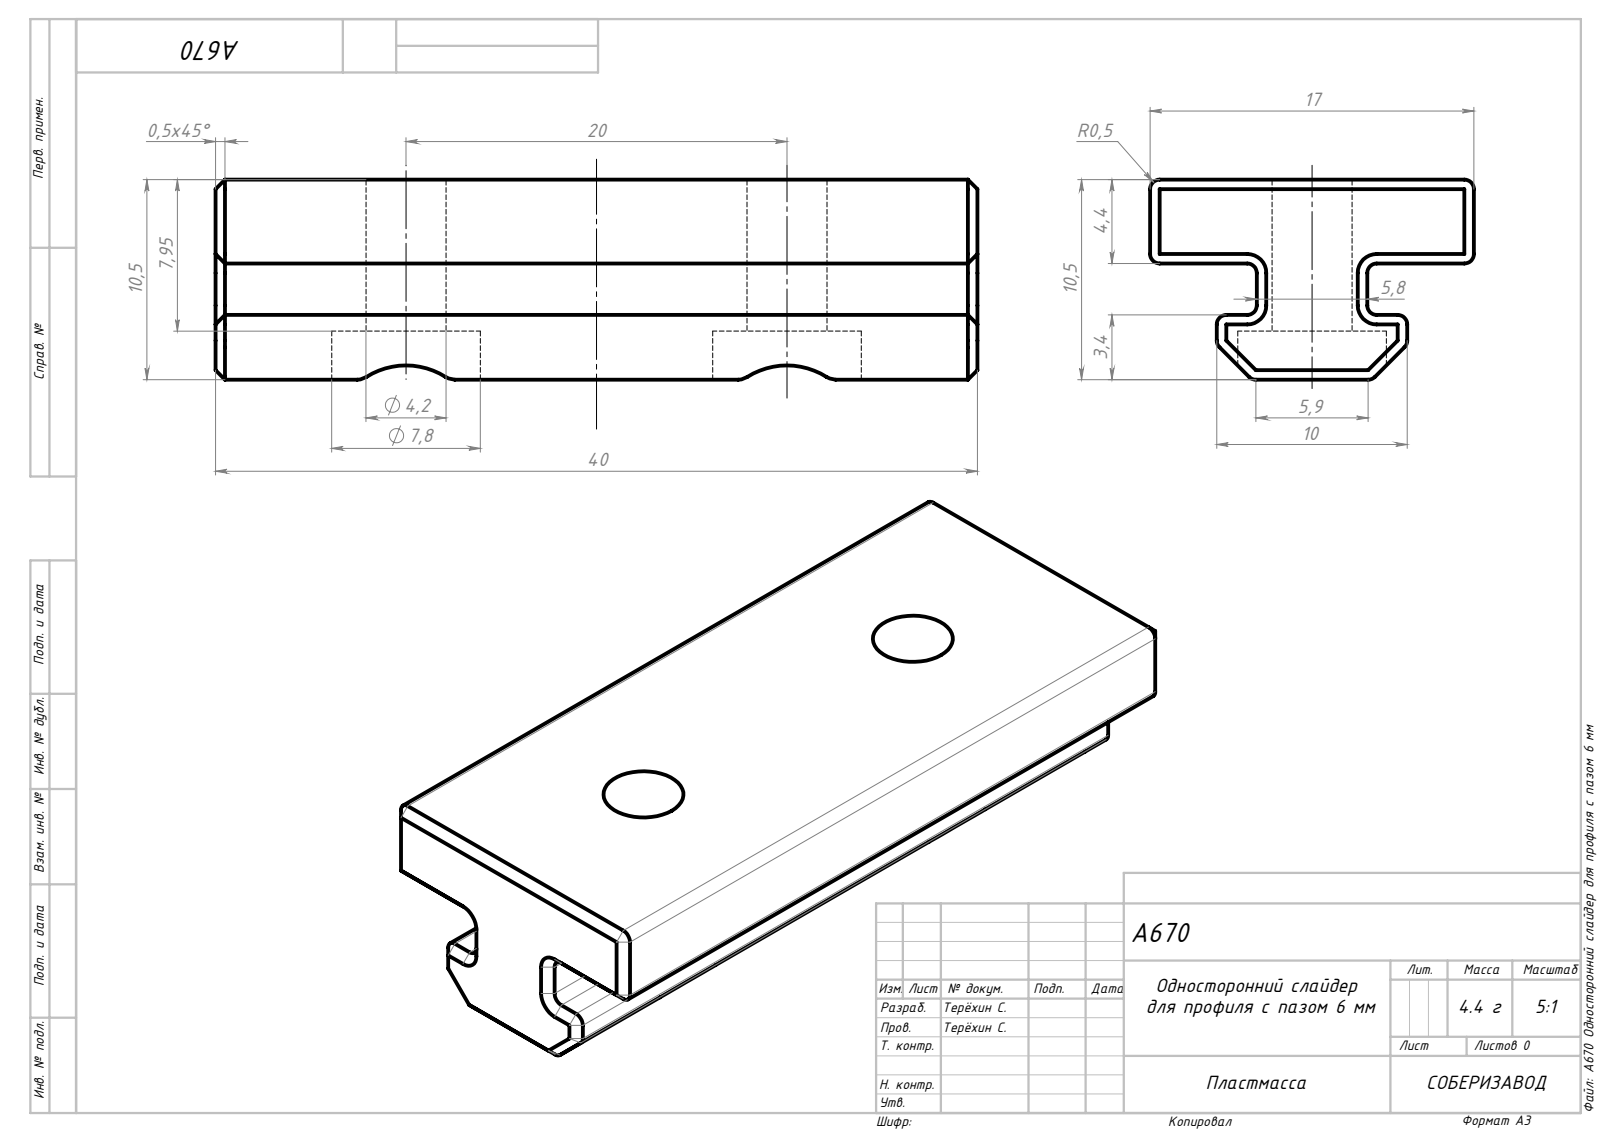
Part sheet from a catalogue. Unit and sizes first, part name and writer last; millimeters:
Units: millimetres
Overall size (bounding box): 40 × 20 × 10.5
Round holes (diameter × count): ⌀4.2 ×2, ⌀7.8 ×2
Partial cylindrical surfaces — rounded edges, fillets, slot ends (radius × count): R0.5 ×14
Main face-to-face distances: 4.7, 5.8, 10.5, 20, 40, 7.25, 12.75, 3.5, 2.3, 7
Hole centre spacings: 20
Volume: 5 047 mm³ · Surface area: 3 127 mm²
Bodies: 1 solid, 102 faces (48 planar, 26 cylindrical, 28 other)
Part name (STEP PRODUCT): Односторонний слайдер 6 паз
STEP written by: SolidWorks 2021 (AUTOMOTIVE_DESIGN)
